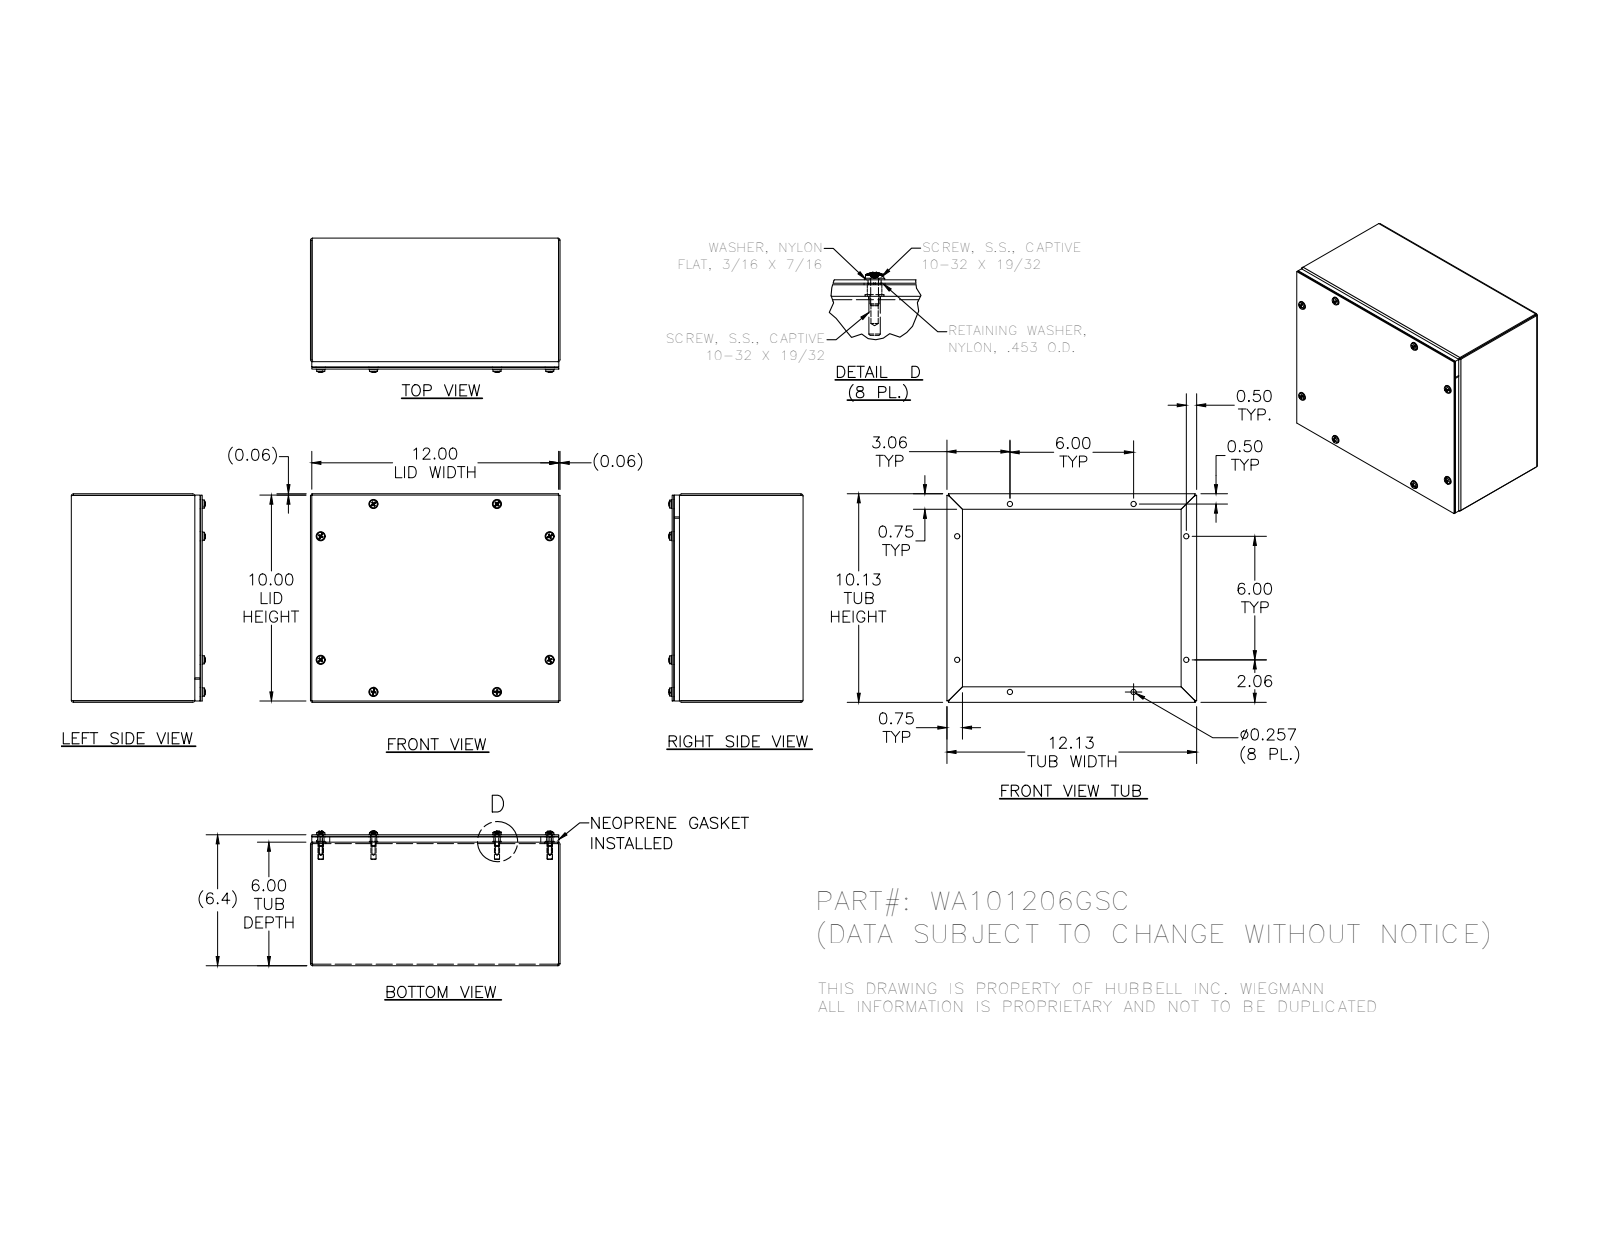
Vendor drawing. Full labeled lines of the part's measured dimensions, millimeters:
Part name (STEP PRODUCT): WA101206GSCBKP; WA101206GSC; 39077; WA1012GSC_LP (+4 more)
STEP written by: SolidWorks 2014 (AUTOMOTIVE_DESIGN)
Units: millimetres
Bodies: 35 solids, 876 faces (416 planar, 232 cylindrical, 228 other)
Overall size (bounding box): 308 × 257.2 × 165.4
Volume: 790 200 mm³ · Surface area: 760 600 mm²
Round holes (diameter × count): ⌀4.8 ×8, ⌀6.5 ×8, ⌀7.1 ×8, ⌀7.1 ×8, ⌀8 ×8, ⌀4 ×7, ⌀5 ×7
Round bosses / shafts (diameter × count): ⌀11.5 ×8, ⌀11.1 ×8, ⌀4.2 ×8, ⌀10.3 ×7, ⌀6.3 ×7
Partial cylindrical surfaces — rounded edges, fillets, slot ends (radius × count): R0.8 ×8, R2.3 ×8, R2.7 ×8
Main face-to-face distances: 1.9, 159.6, 255.3, 161.4, 157.7, 306.1, 9, 150.5, 257.2, 253.4
Hole centre spacings: 152.4, 221.1, 290.2, 76.2, 202.8, 202.8, 290.2, 76.2
